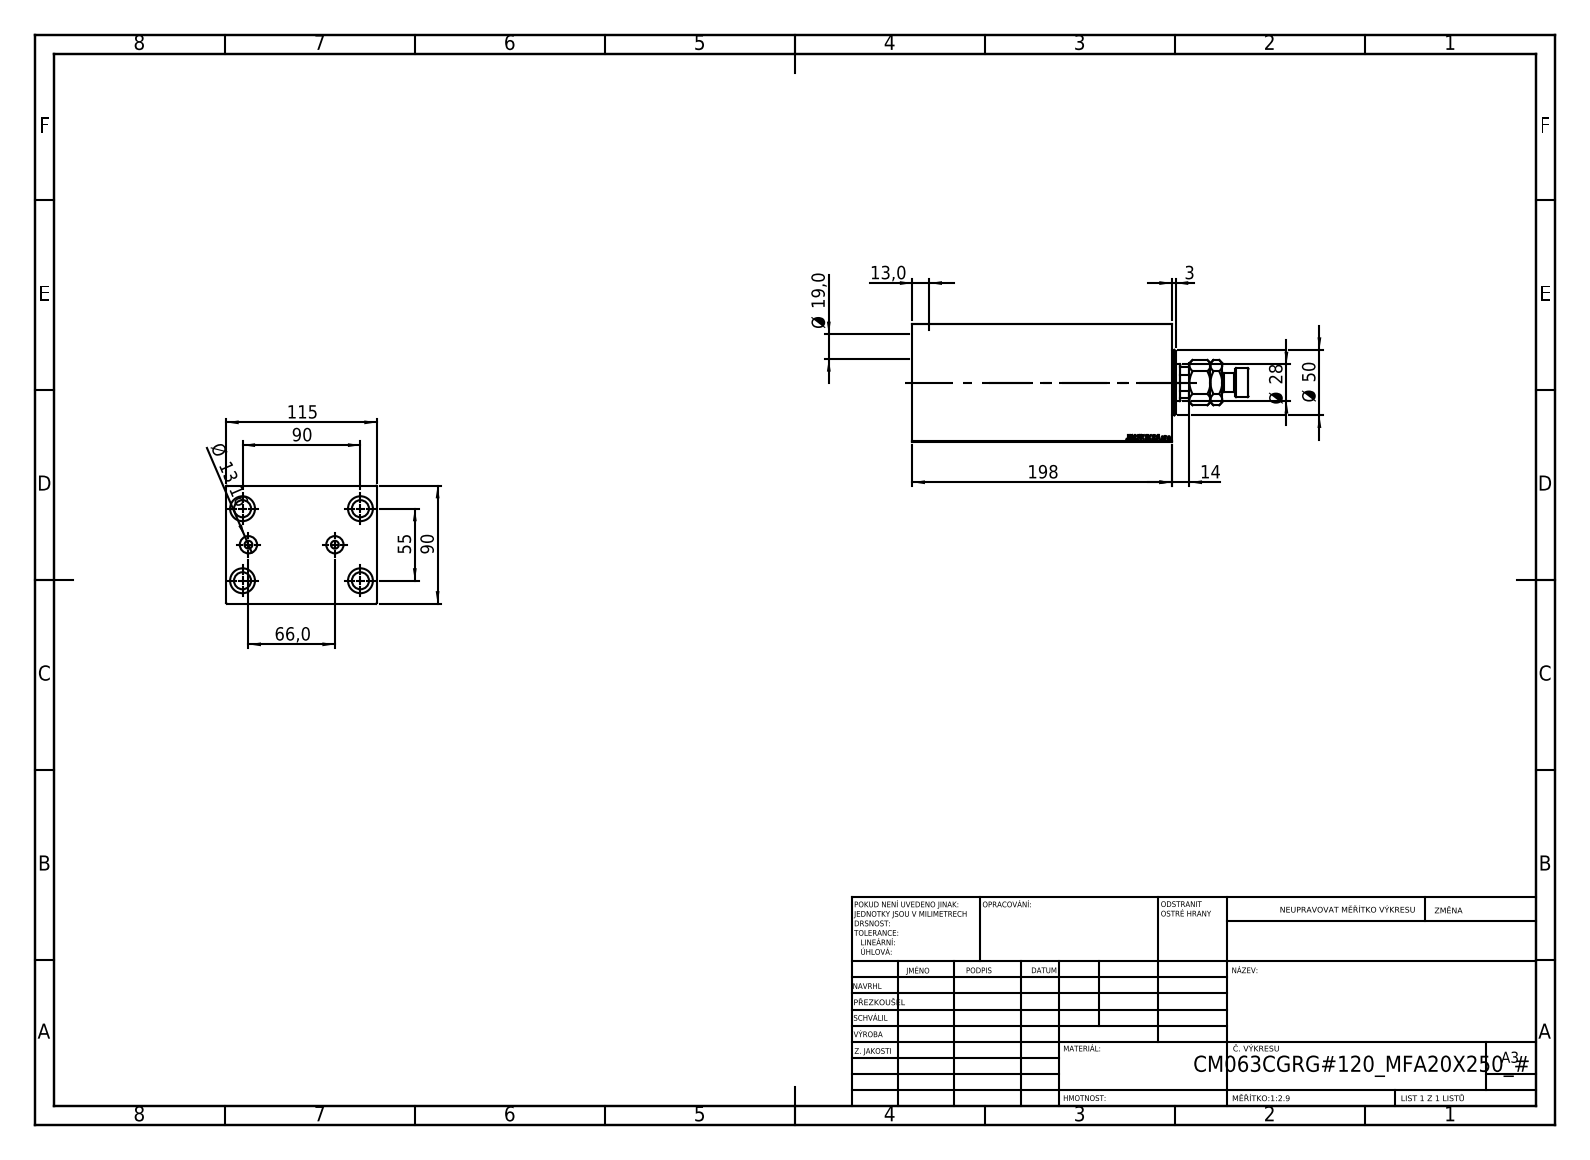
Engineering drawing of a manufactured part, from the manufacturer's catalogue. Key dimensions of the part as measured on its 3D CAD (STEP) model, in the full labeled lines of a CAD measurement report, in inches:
Part name (STEP PRODUCT): MFA; V450CM_VC_B; V450CM_C_VCP; V450CM_C_Body
STEP written by: SolidWorks 2019 (CONFIG_CONTROL_DESIGN)
Units: inches
Bodies: 4 solids, 912 faces (424 planar, 62 cylindrical, 426 other)
Overall size (bounding box): 10.098 × 4.528 × 3.543
Volume: 100.6 in³ · Surface area: 344.6 in²
Round holes (diameter × count): ⌀0.512 ×4, ⌀0.748 ×4, ⌀0.236 ×2, ⌀0.518 ×2, ⌀0.728 ×1, ⌀1.102 ×1, ⌀1.24 ×1, ⌀2.48 ×1, ⌀2.559 ×1, ⌀2.835 ×1
Round bosses / shafts (diameter × count): ⌀1.969 ×1, ⌀0.866 ×1, ⌀0.551 ×1
Partial cylindrical surfaces — rounded edges, fillets, slot ends (radius × count): R0.531 ×1
Main face-to-face distances: 3.543, 4.528, 7.795, 0.689, 7.106, 0.531, 6.575, 7.264, 1.85, 2.539
Hole centre spacings: 2.076, 1.097, 1.327, 2.165, 2.979, 3.536, 3.543, 4.153
